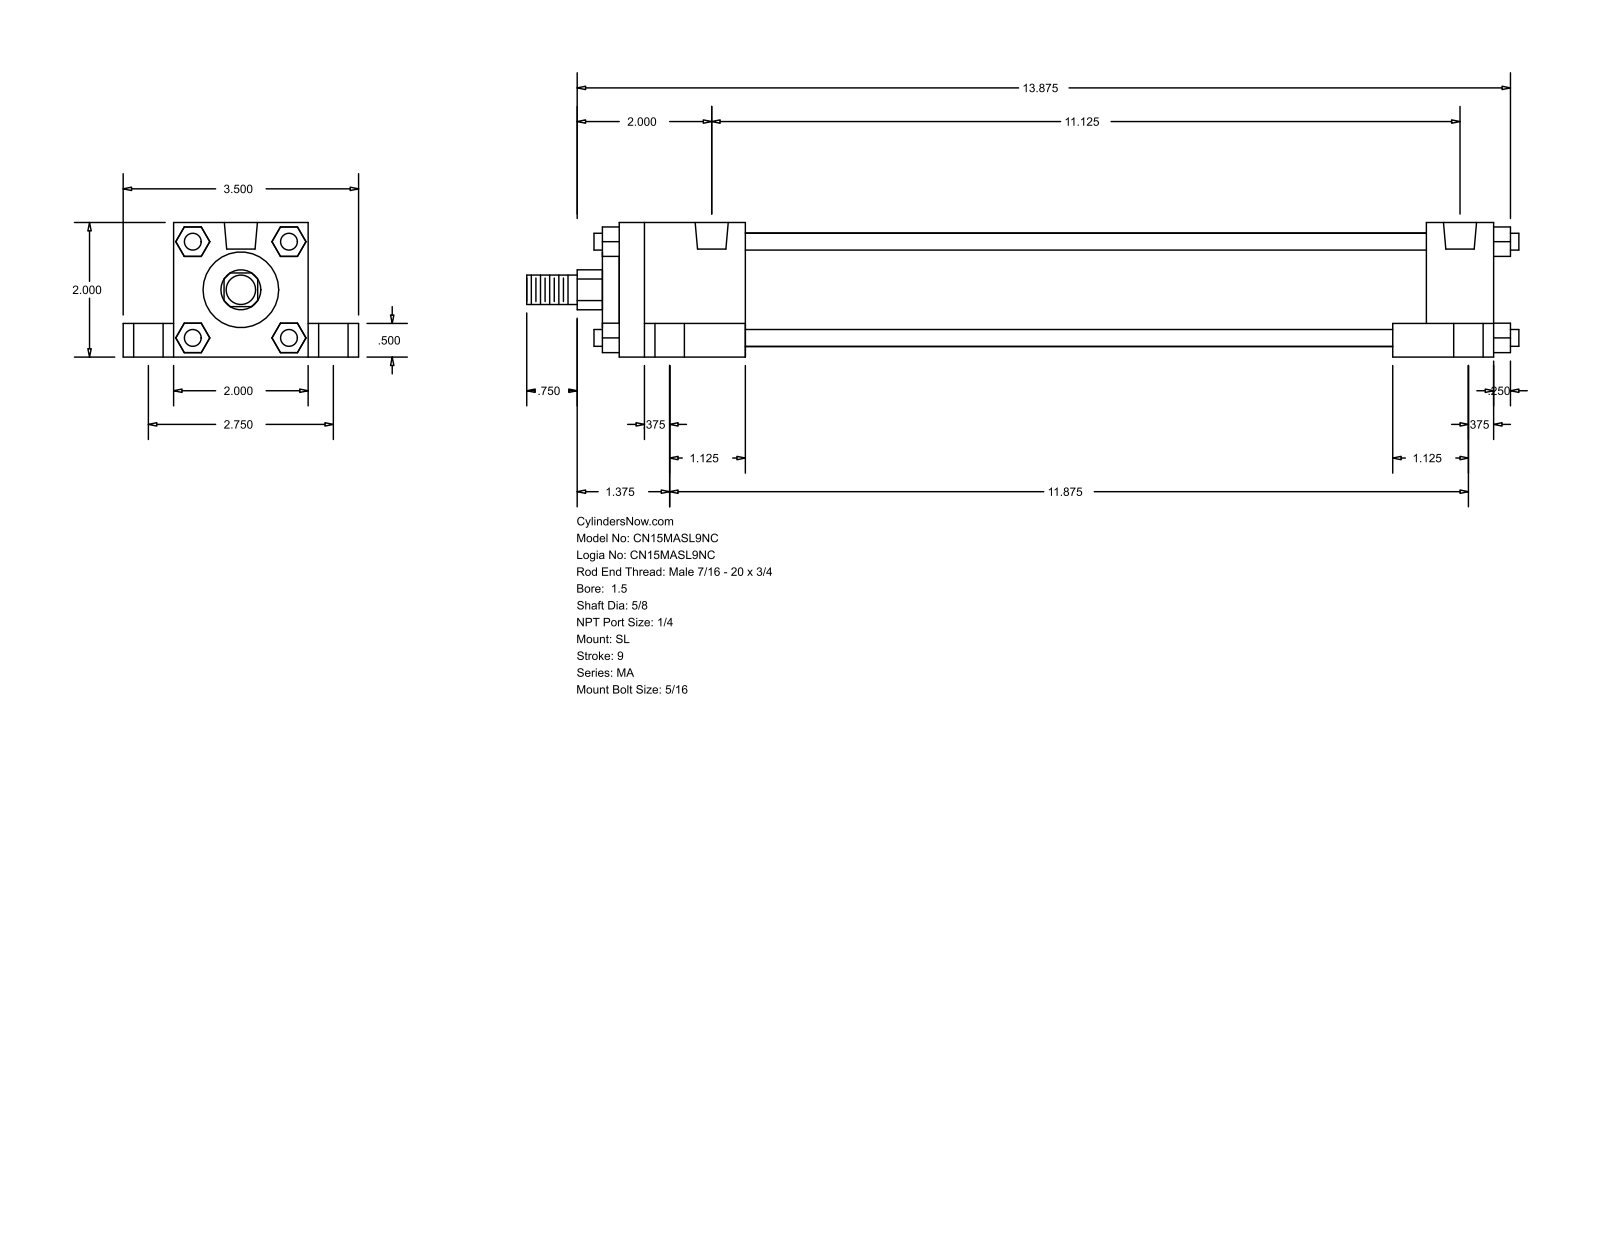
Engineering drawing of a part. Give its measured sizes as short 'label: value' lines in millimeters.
name: MA_SL__0150_0.625
written by: GSSL Pune (CONFIG_CONTROL_DESIGN)
unit: mm
bodies: 0 solids, 148 faces (112 planar, 36 cylindrical, 0 other)
size: 374.65 × 88.9 × 50.8
holes: 4× ⌀7.94, 4× ⌀11.11, 4× ⌀17.46, 2× ⌀12.49
bosses: 4× ⌀6.35, 1× ⌀42.93, 1× ⌀28.57, 1× ⌀15.88, 1× ⌀11.11
rounds: 1× R7.54
face distances: 50.8, 19.05, 38.1, 69.85, 12.7, 330.19, 9.52, 304.8, 25.39, 47.62
hole spacings: 35.06, 38.36, 69.84, 282.58, 287.88, 300.5, 301.63, 309.61
